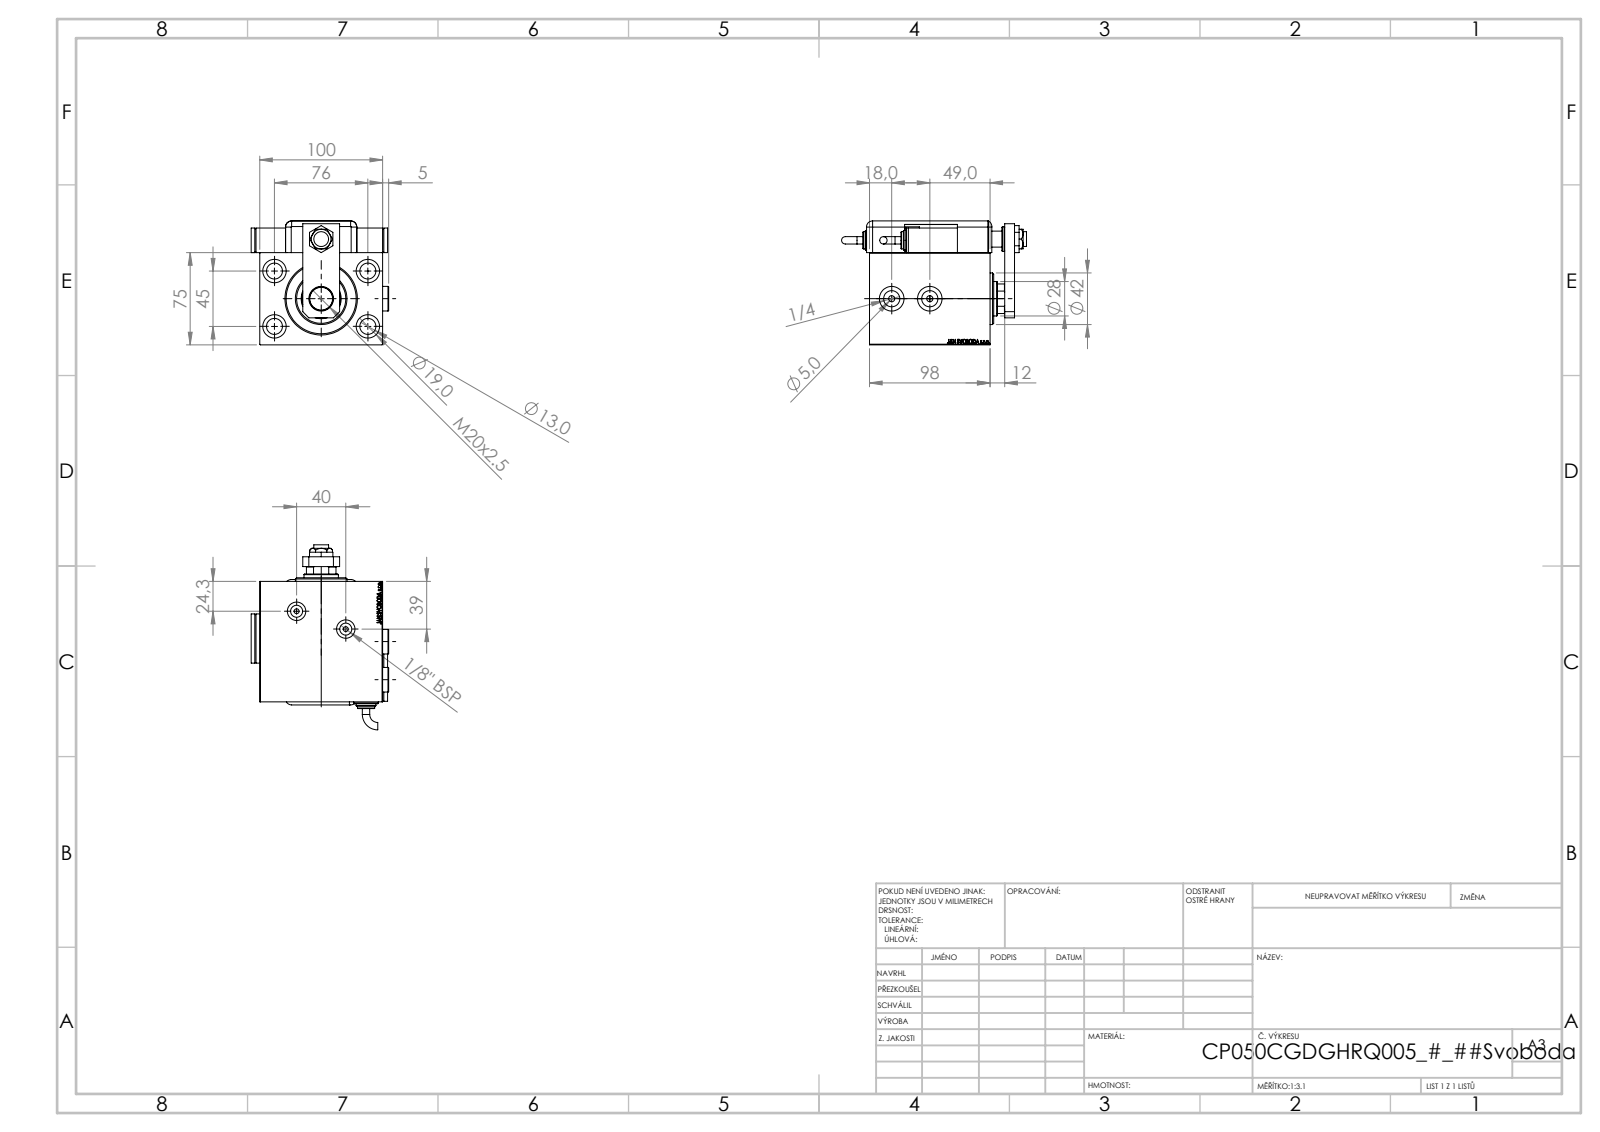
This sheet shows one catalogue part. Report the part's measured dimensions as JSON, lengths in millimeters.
{"part_name": "ZARAZKA_Q; SWITCH Q; NUT_D13; V450CP_C (+7 more)", "step_written_by": "SolidWorks 2019 (CONFIG_CONTROL_DESIGN)", "units": "millimeters", "bodies": {"solids": 15, "faces": 1327, "planar": 655, "cylindrical": 147, "other": 525}, "overall_size": [150.46, 111.9, 100.8], "volume_mm3": 796861, "surface_area_mm2": 171999, "round_holes": [[13, 5], [4, 4], [19, 4], [20, 3], [5, 2], [8, 2], [9.73, 2], [13.16, 2], [15, 2], [12, 1], [14, 1], [18.5, 1]], "round_bosses_or_shafts": [[20, 3], [16, 2], [14, 2], [6, 2], [42, 1]], "partial_cylinders_radius": [[5, 9], [10, 1], [13.5, 1]], "face_to_face_distances": [75, 3, 100, 98, 14, 20, 49, 84, 25.8, 100.8], "hole_center_spacings": [44.16, 45, 46.04, 76, 80.53, 88.32, 18.28, 20]}
